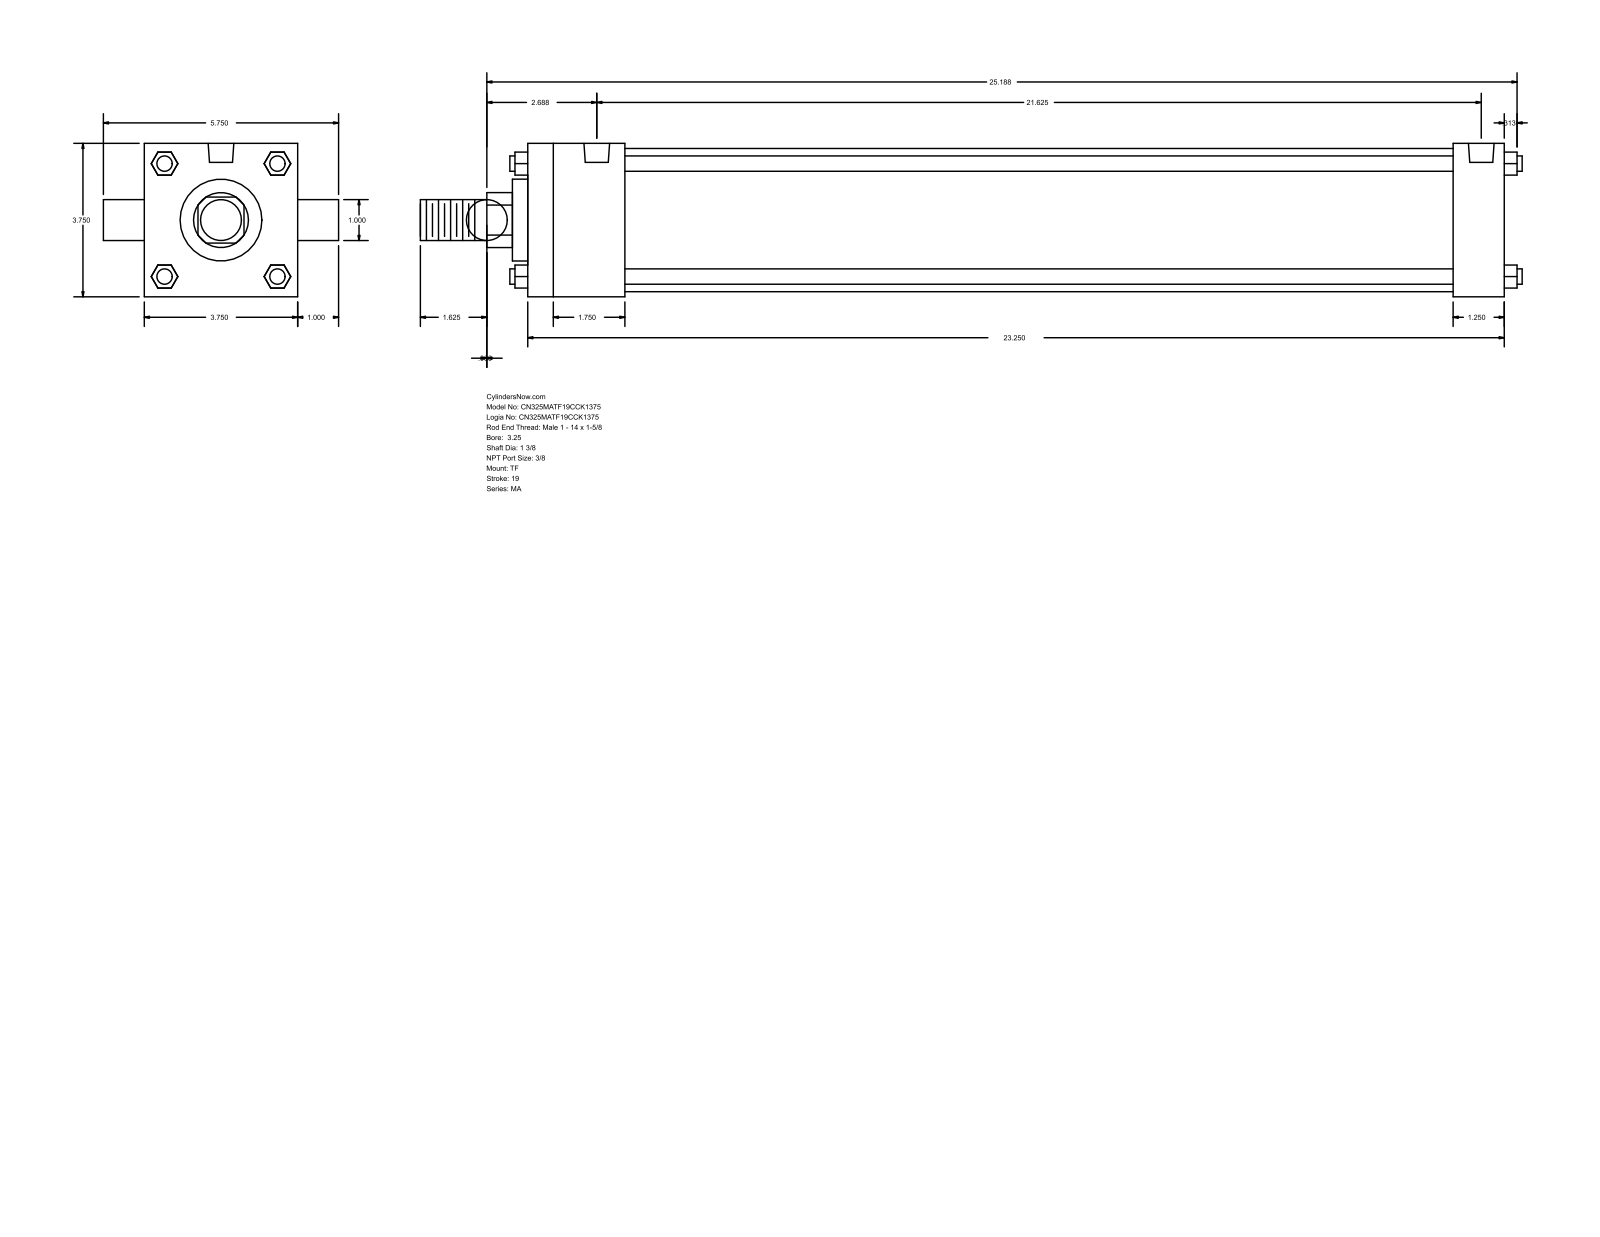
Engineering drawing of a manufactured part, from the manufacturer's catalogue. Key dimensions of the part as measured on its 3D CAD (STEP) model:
Part name (STEP PRODUCT): MA_TF__0325_1.375
STEP written by: GSSL Pune (CONFIG_CONTROL_DESIGN)
Units: millimetres
Bodies: 0 solids, 120 faces (92 planar, 28 cylindrical, 0 other)
Overall size (bounding box): 684.21 × 146.05 × 95.25
Round holes (diameter × count): ⌀11.11 ×3, ⌀15.93 ×2
Round bosses / shafts (diameter × count): ⌀9.53 ×4, ⌀25.4 ×2, ⌀88.9 ×1, ⌀50.8 ×1, ⌀34.92 ×1
Partial cylindrical surfaces — rounded edges, fillets, slot ends (radius × count): R17.06 ×1
Main face-to-face distances: 95.24, 606.43, 60.32, 574.68, 514.36, 546.11, 31.75, 9.52, 69.84, 584.2
Hole centre spacings: 4.77, 544.51, 539.74, 549.28
